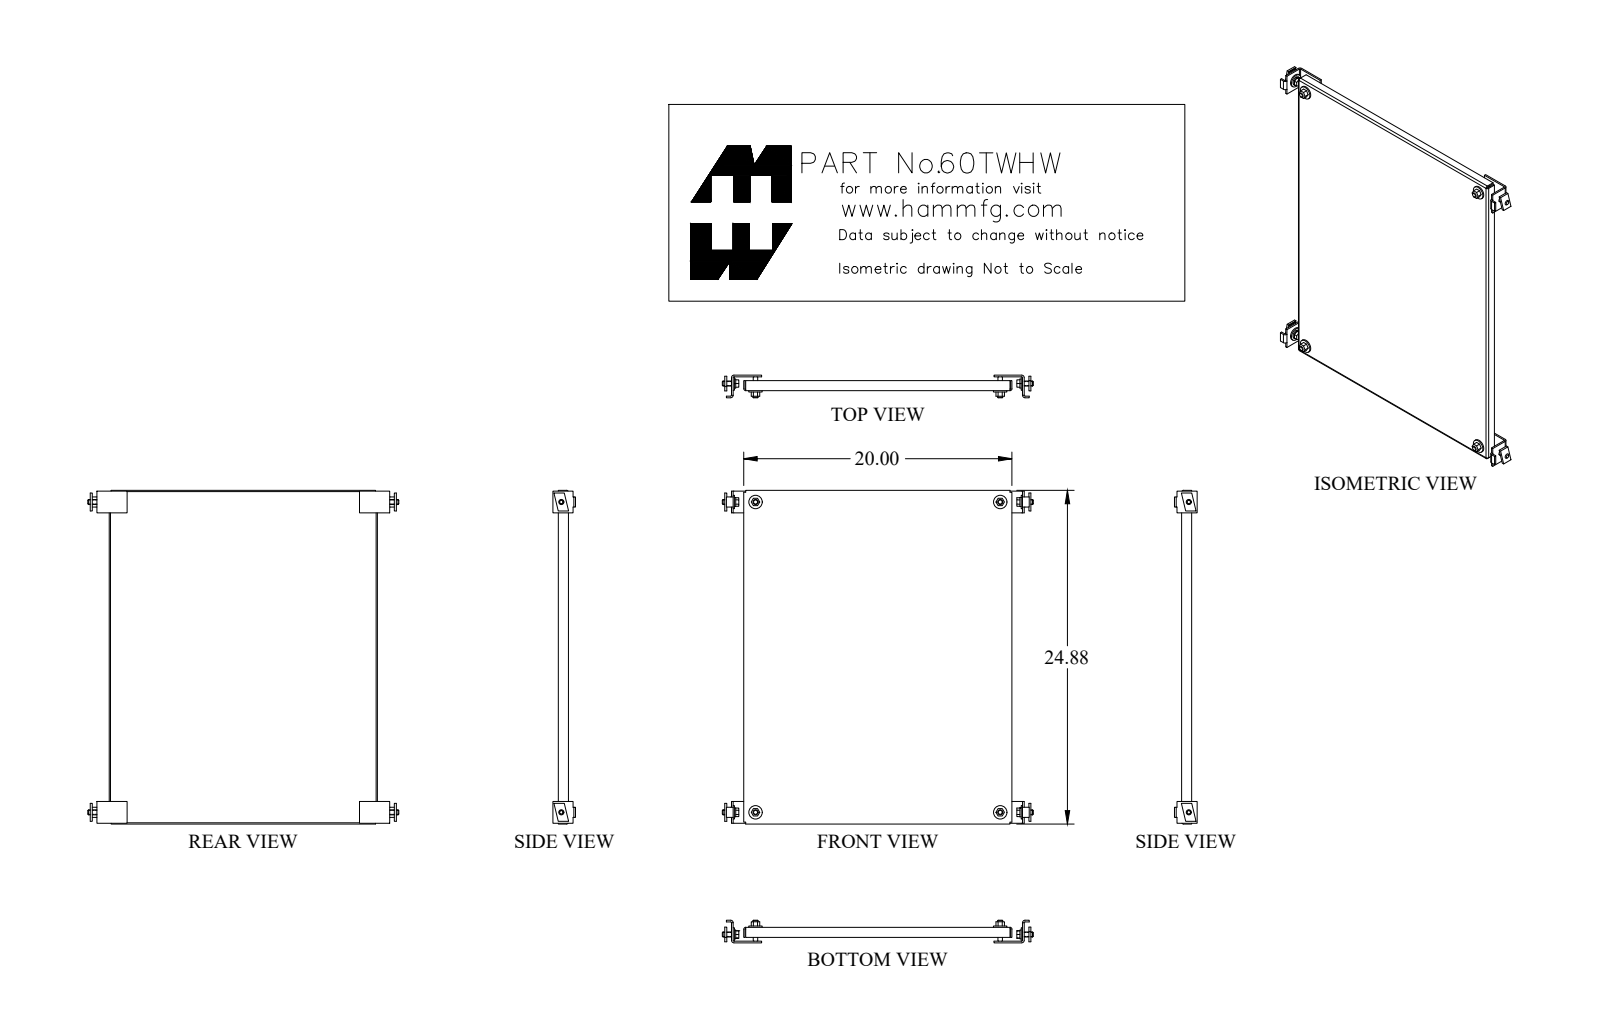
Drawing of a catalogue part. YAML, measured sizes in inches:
part_name: "60TWHW_Default"
step_written_by: "SolidWorks 2018 (CONFIG_CONTROL_DESIGN)"
units: inches
bodies: {solids: 1, faces: 38, planar: 22, cylindrical: 16, other: 0}
overall_size: [24.875, 20, 0.75]
volume: 52.33
surface_area: 1111
round_holes:
  - {diameter: 0.563, count: 4}
partial_cylinders:
  - {radius: 0.048, count: 4}
  - {radius: 0.143, count: 4}
face_to_face_distances: [0.095, 19.905, 24.78, 19.81, 20, 24.875, 24.685, 0.75, 0.655, 0.143]
hole_center_spacings: [18.25, 23.125, 29.459]
